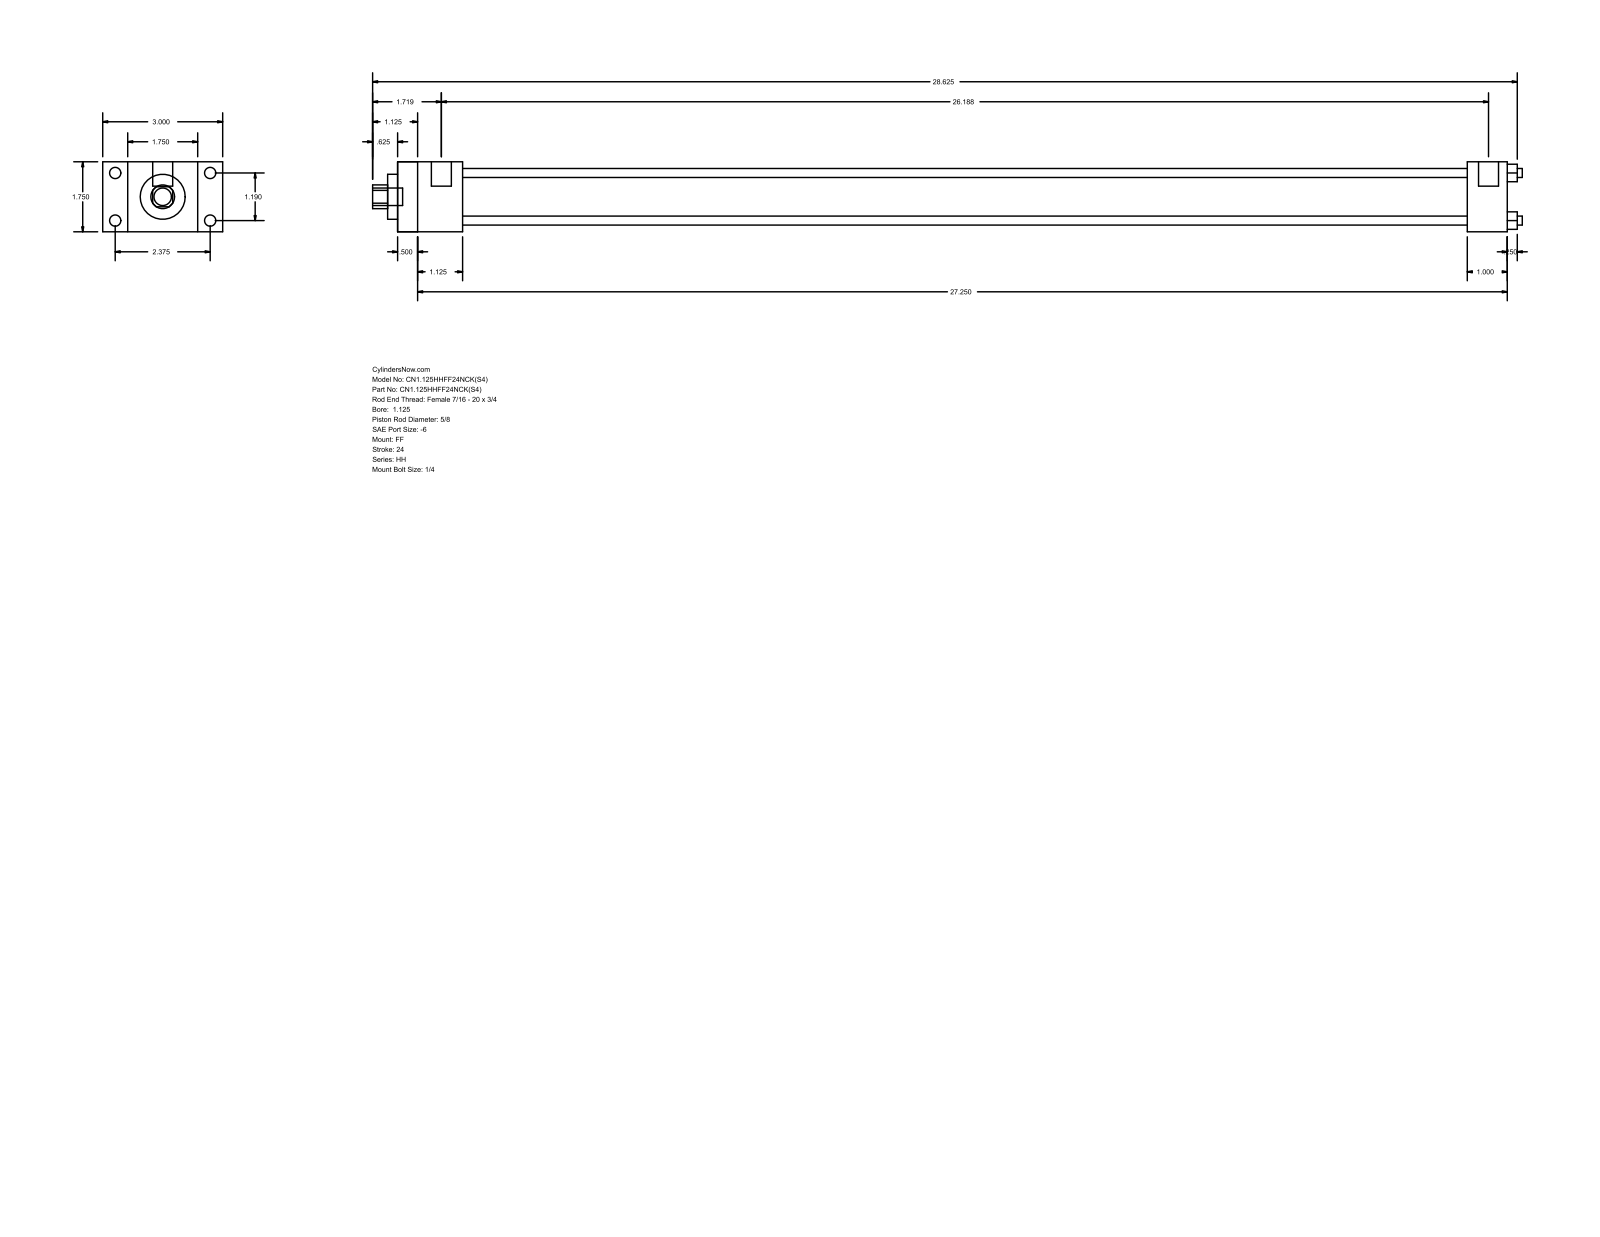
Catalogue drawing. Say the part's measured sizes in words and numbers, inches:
The part is named "HH_FF__0112_0.625". Its 3-D file was written by "GSSL Pune (CONFIG_CONTROL_DESIGN)". It is 0 solids with 92 faces: 64 planar, 28 cylindrical and 0 other. Overall it measures 28.75 by 3 by 1.75 inches. Round holes: 4 of diameter 0.225, 1 of diameter 0.625, 1 of diameter 1.125, 1 of diameter 1.375. Round bosses or shafts: 4 of diameter 0.281, 4 of diameter 0.219, 2 of diameter 0.5, 1 of diameter 0.437. Partial cylindrical surfaces (rounded edges, fillets, slot ends): 1 of radius 0.297. The main face-to-face distances are 1.75, 27.75, 0.625, 0.5, 27.25, 2.375, 1.125, 1.625, 26.75, 26.25. The hole center spacings are 0.841, 1.19, 1.683.
